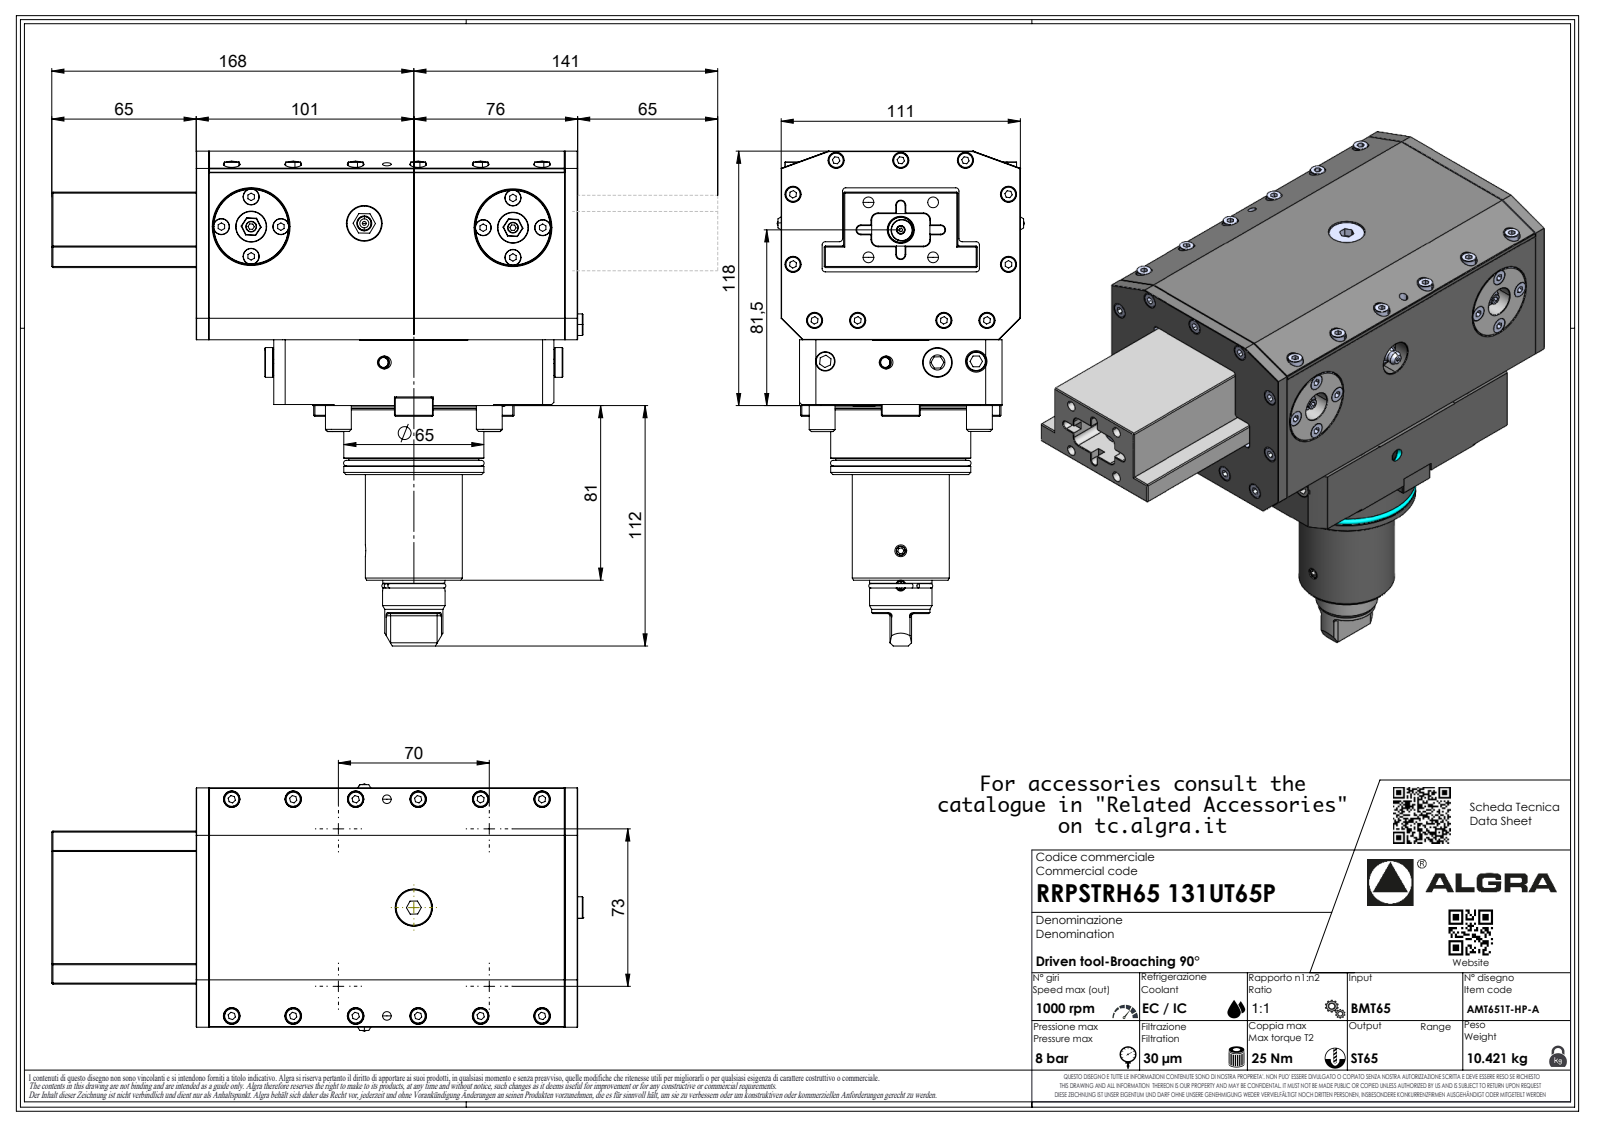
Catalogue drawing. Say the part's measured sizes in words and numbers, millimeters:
The part is named "RRPSTRH65131UT65P". Its 3-D file was written by "SolidWorks 2023 (AUTOMOTIVE_DESIGN)". It is 1 solid with 782 faces: 515 planar, 110 cylindrical and 157 other. Overall it measures 246.47 by 229.5 by 114.6 millimeters. Its volume is 2 375 000 cubic millimeters and its surface area 133 116 square millimeters. Round holes: 1 of diameter 2.1, 1 of diameter 5.5, 1 of diameter 61. Round bosses or shafts: 1 of diameter 65, 1 of diameter 64.6, 1 of diameter 60.3, 1 of diameter 55, 1 of diameter 45, 1 of diameter 29, 1 of diameter 27, 1 of diameter 10. Partial cylindrical surfaces (rounded edges, fillets, slot ends): 12 of radius 3, 12 of radius 3.5, 7 of radius 0.33, 7 of radius 0.52, 7 of radius 3.7, 6 of radius 1, 4 of radius 10, 4 of radius 10.5. The main face-to-face distances are 111, 177, 8.5, 102.5, 87.5, 30.5, 54, 33.5, 118, 73.5.
